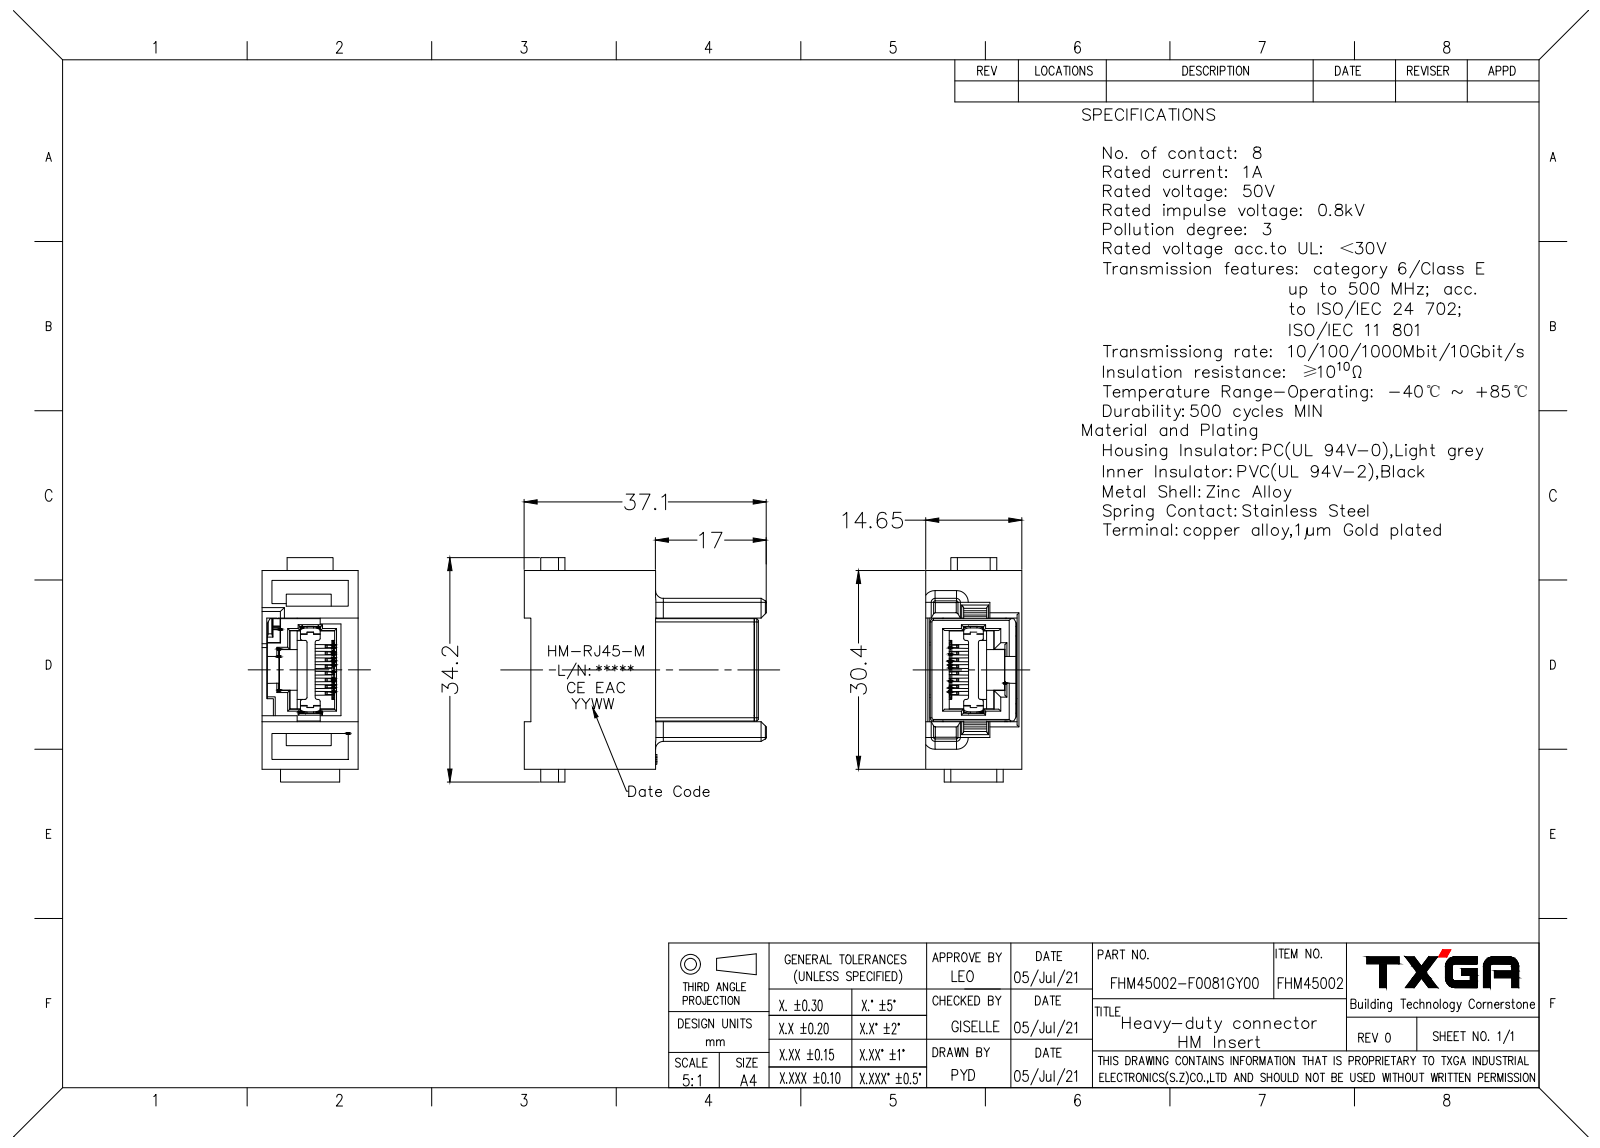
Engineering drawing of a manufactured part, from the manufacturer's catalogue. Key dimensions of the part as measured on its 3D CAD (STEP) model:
Part name (STEP PRODUCT): FHM45002-F0081GY00
STEP written by: SolidWorks 2021 (CONFIG_CONTROL_DESIGN)
Units: millimetres
Bodies: 1 solid, 592 faces (402 planar, 119 cylindrical, 71 other)
Overall size (bounding box): 36.9 × 34.2 × 14.6
Volume: 6 972 mm³ · Surface area: 10 322 mm²
Partial cylindrical surfaces — rounded edges, fillets, slot ends (radius × count): R0.5 ×33, R0.3 ×28, R0.1 ×12, R0.2 ×12, R0.4 ×5, R0.15 ×4, R1 ×3, R0.45 ×2
Main face-to-face distances: 15.65, 0.55, 1.9, 1.2, 1.75, 14.6, 1.5, 7.25, 7.4, 22.9
